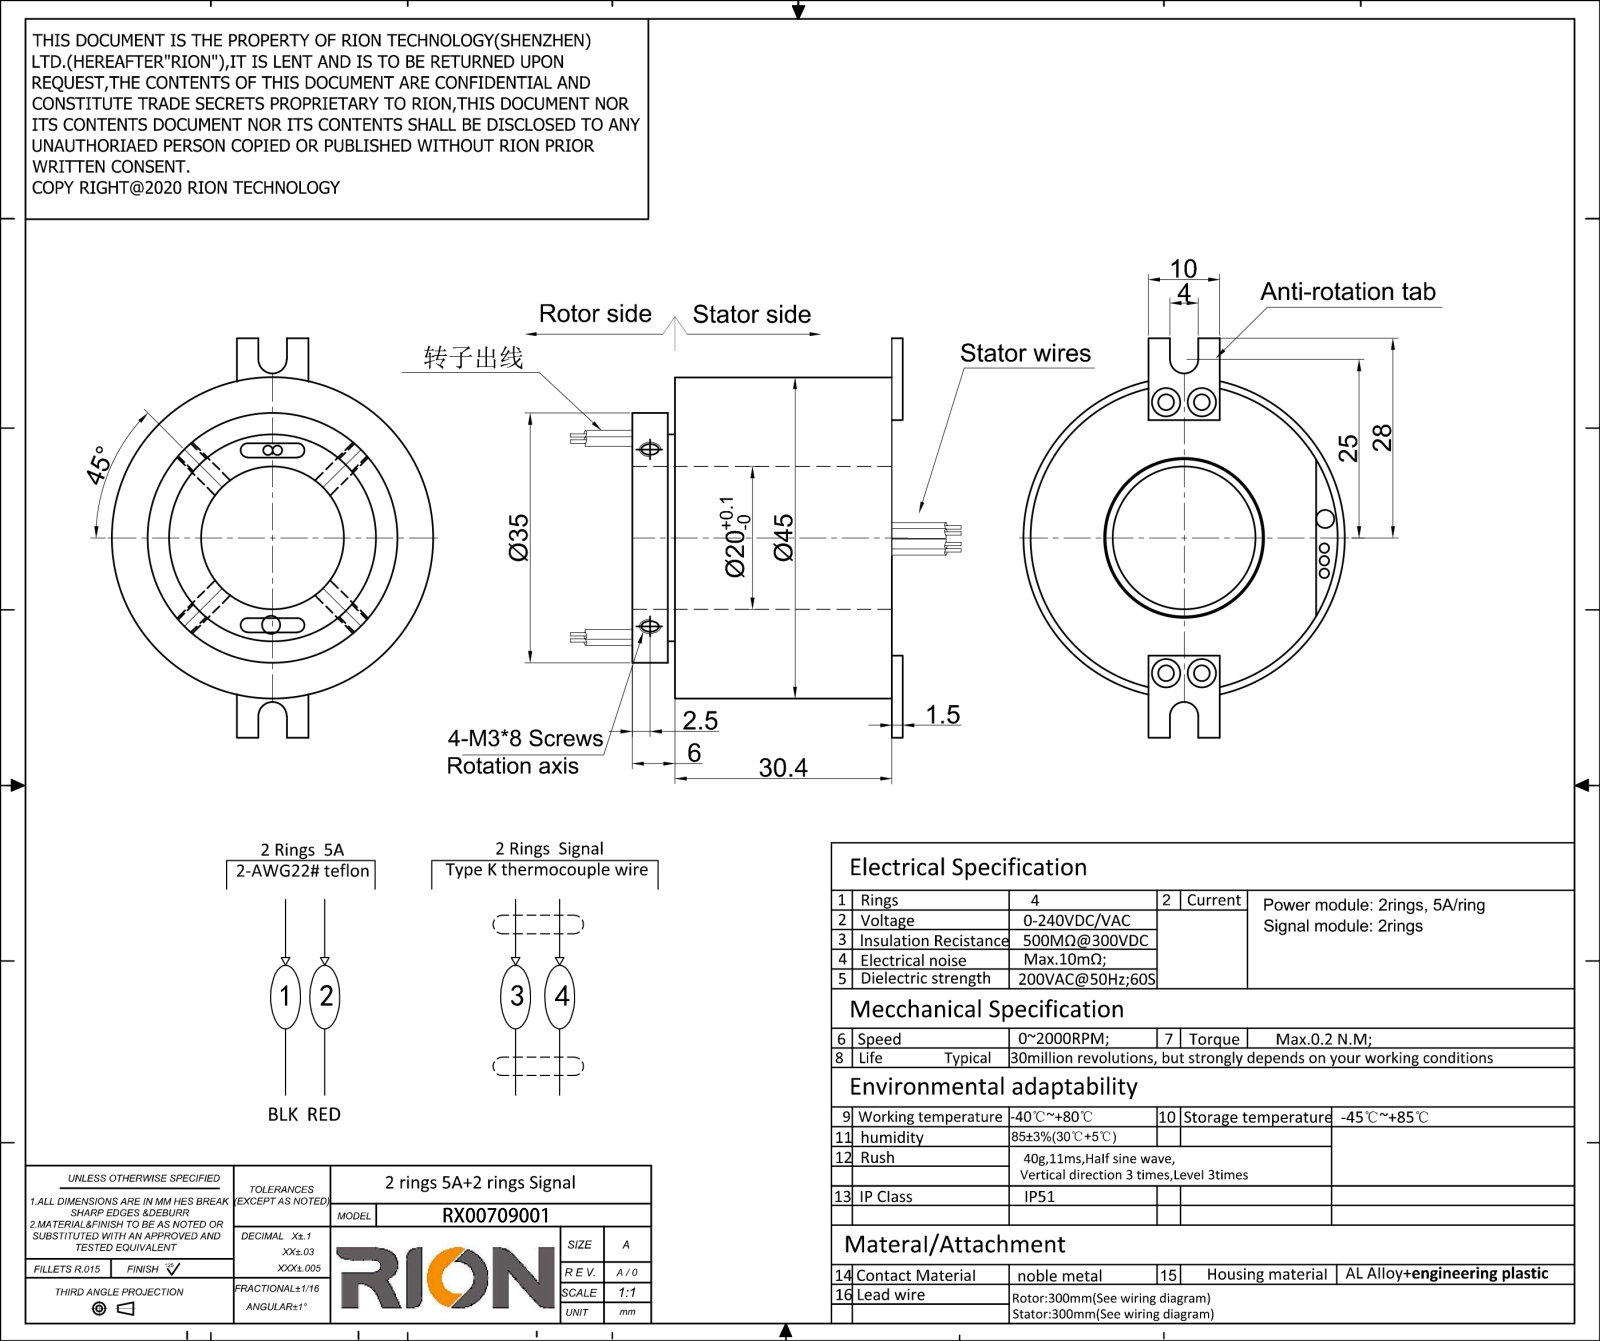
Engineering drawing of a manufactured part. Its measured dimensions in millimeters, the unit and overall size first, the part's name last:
Units: millimetres
Overall size (bounding box): 56 × 54.4 × 45
Round holes (diameter × count): ⌀1.6 ×4, ⌀2.2 ×4, ⌀2.5 ×4, ⌀20 ×1, ⌀22.2 ×1, ⌀43 ×1
Round bosses / shafts (diameter × count): ⌀2.5 ×2, ⌀1.3 ×2, ⌀1.25 ×2, ⌀45 ×1, ⌀42.9 ×1, ⌀35 ×1, ⌀29 ×1, ⌀22 ×1
Partial cylindrical surfaces — rounded edges, fillets, slot ends (radius × count): R1 ×4, R2 ×2
Main face-to-face distances: 30.4, 6, 36.4, 1, 5, 31.4, 37.9, 32.9, 31.9, 1.5
Hole centre spacings: 19.16, 5, 38, 38.33
Volume: 42 455 mm³ · Surface area: 13 288 mm²
Bodies: 1 solid, 132 faces (52 planar, 64 cylindrical, 16 other)
Part name (STEP PRODUCT): GT2045-P0205-S02
STEP written by: SolidWorks 2014 (CONFIG_CONTROL_DESIGN)
